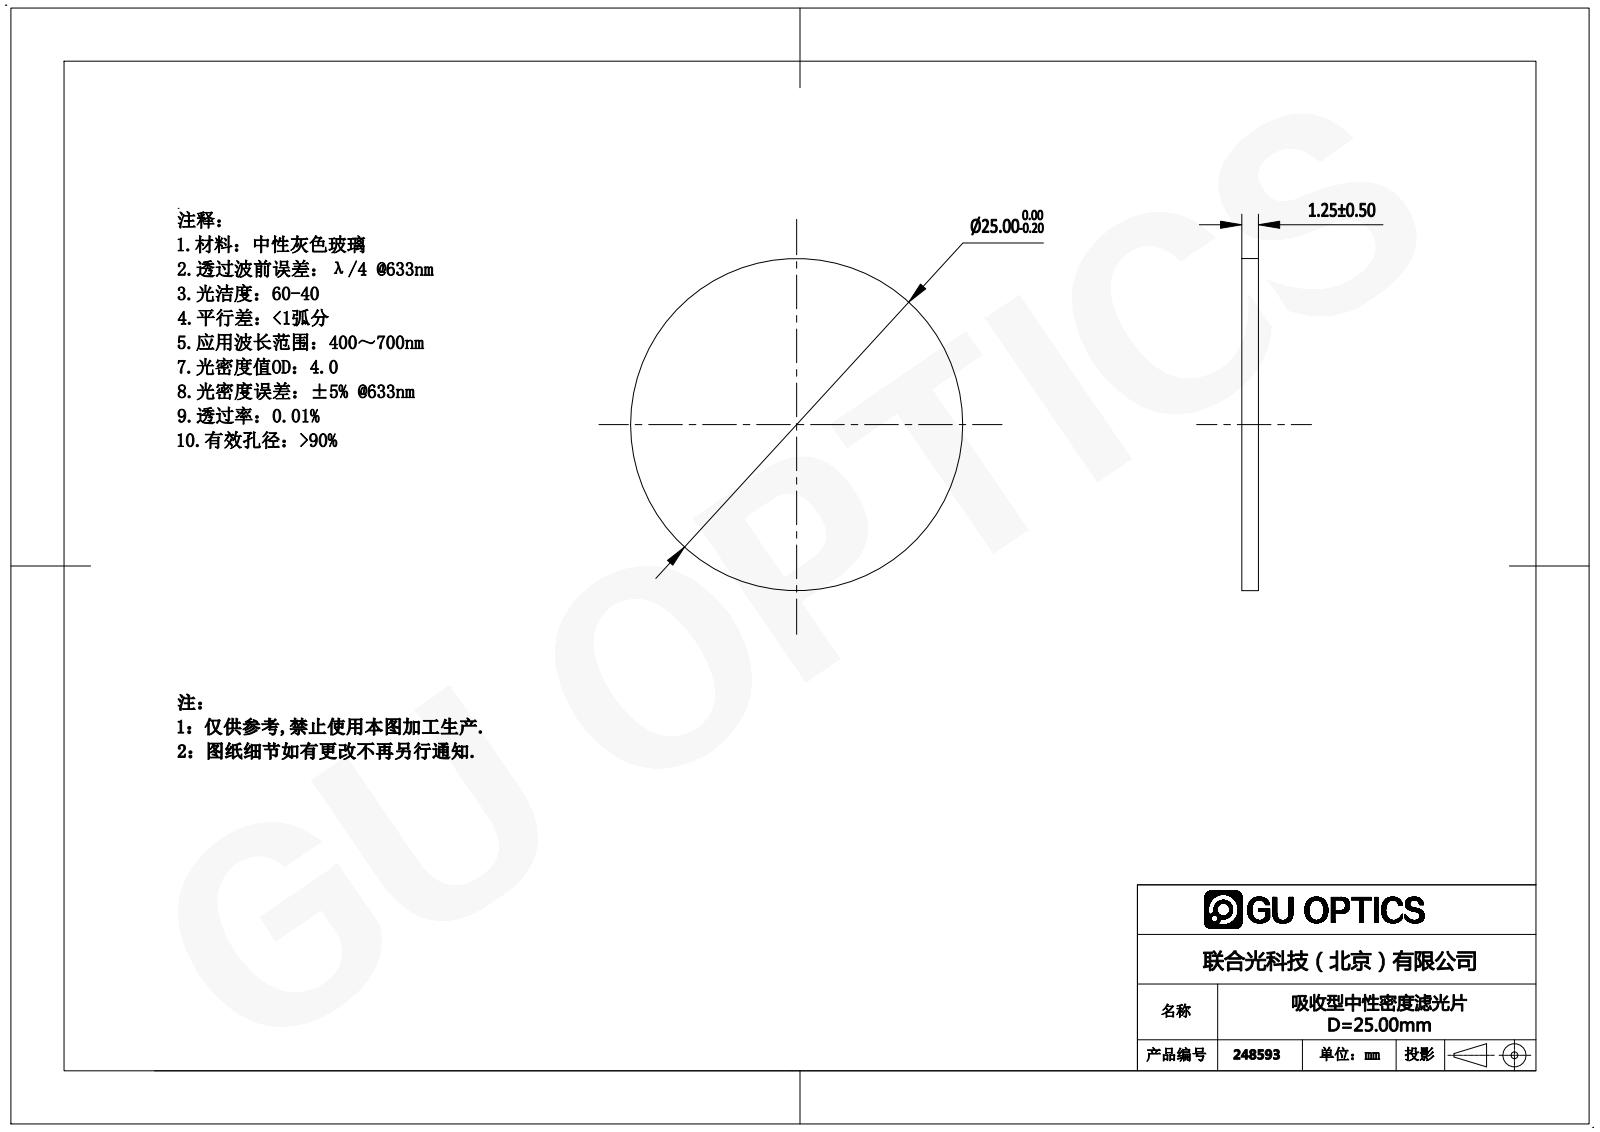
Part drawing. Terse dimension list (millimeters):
name: 248593
written by: SolidWorks 2016 (AUTOMOTIVE_DESIGN)
unit: mm
bodies: 1 solid, 4 faces (2 planar, 2 cylindrical, 0 other)
size: 25 × 25 × 1.25
volume: 614 mm³; area: 1 080 mm²
bosses: 1× ⌀25
face distances: 1.25
